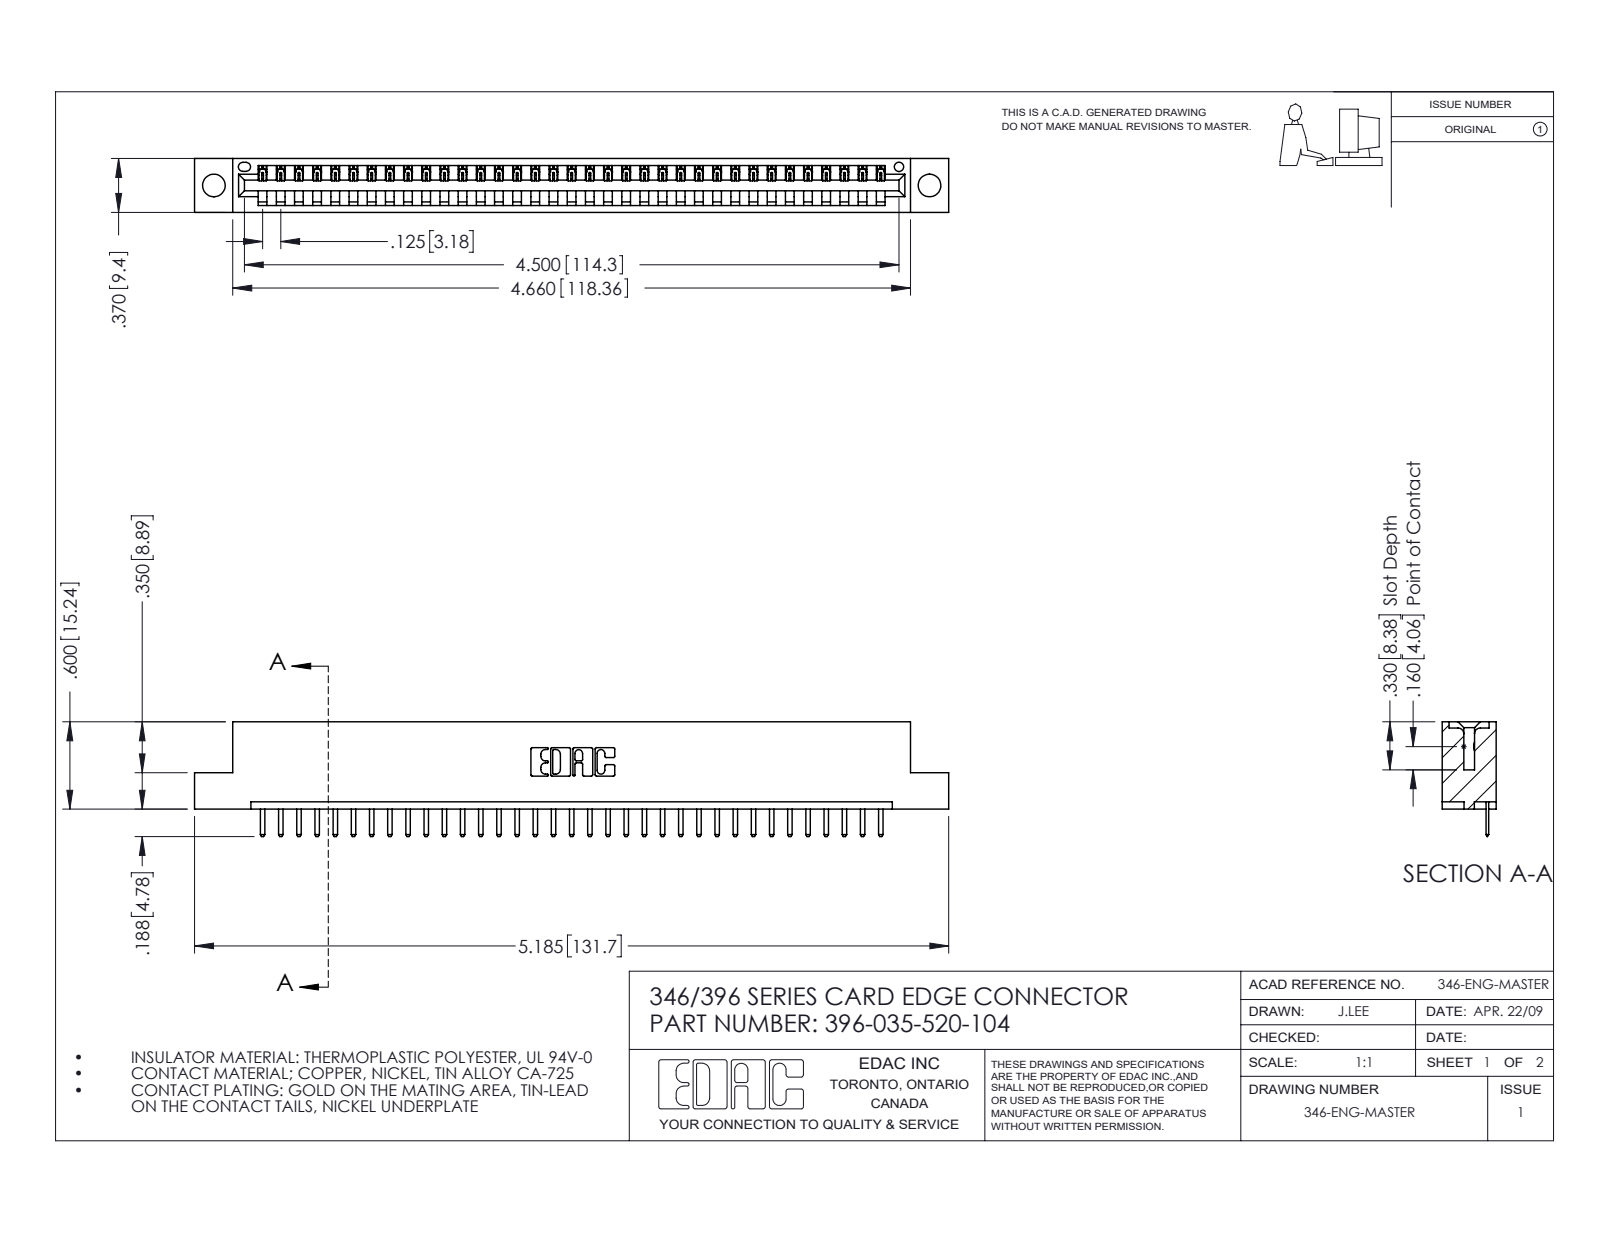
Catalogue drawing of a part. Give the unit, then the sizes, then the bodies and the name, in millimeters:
Units: millimetres
Overall size (bounding box): 131.7 × 20 × 9.4
Round holes (diameter × count): ⌀4 ×2, ⌀1.6 ×1
Partial cylindrical surfaces — rounded edges, fillets, slot ends (radius × count): R0.3 ×72, R0.2 ×70, R0.3 ×22, R0.2 ×6, R0.8 ×6, R0.7 ×3, R0.8 ×2, R1 ×2
Main face-to-face distances: 1.2, 8.2, 9.4, 6.4, 3.8, 5.6, 2.5, 4.4, 1.8, 7.6
Hole centre spacings: 6.2, 119.7, 125
Volume: 12 400 mm³ · Surface area: 14 850 mm²
Bodies: 36 solids, 2292 faces (1546 planar, 746 cylindrical, 0 other)
Part name (STEP PRODUCT): 346 Part_Flush Mounting Lugs - 0.156 Dia-TH; 396-035-520-104; 345-292-001_345-293-120
STEP written by: SolidWorks 2016 (CONFIG_CONTROL_DESIGN)
